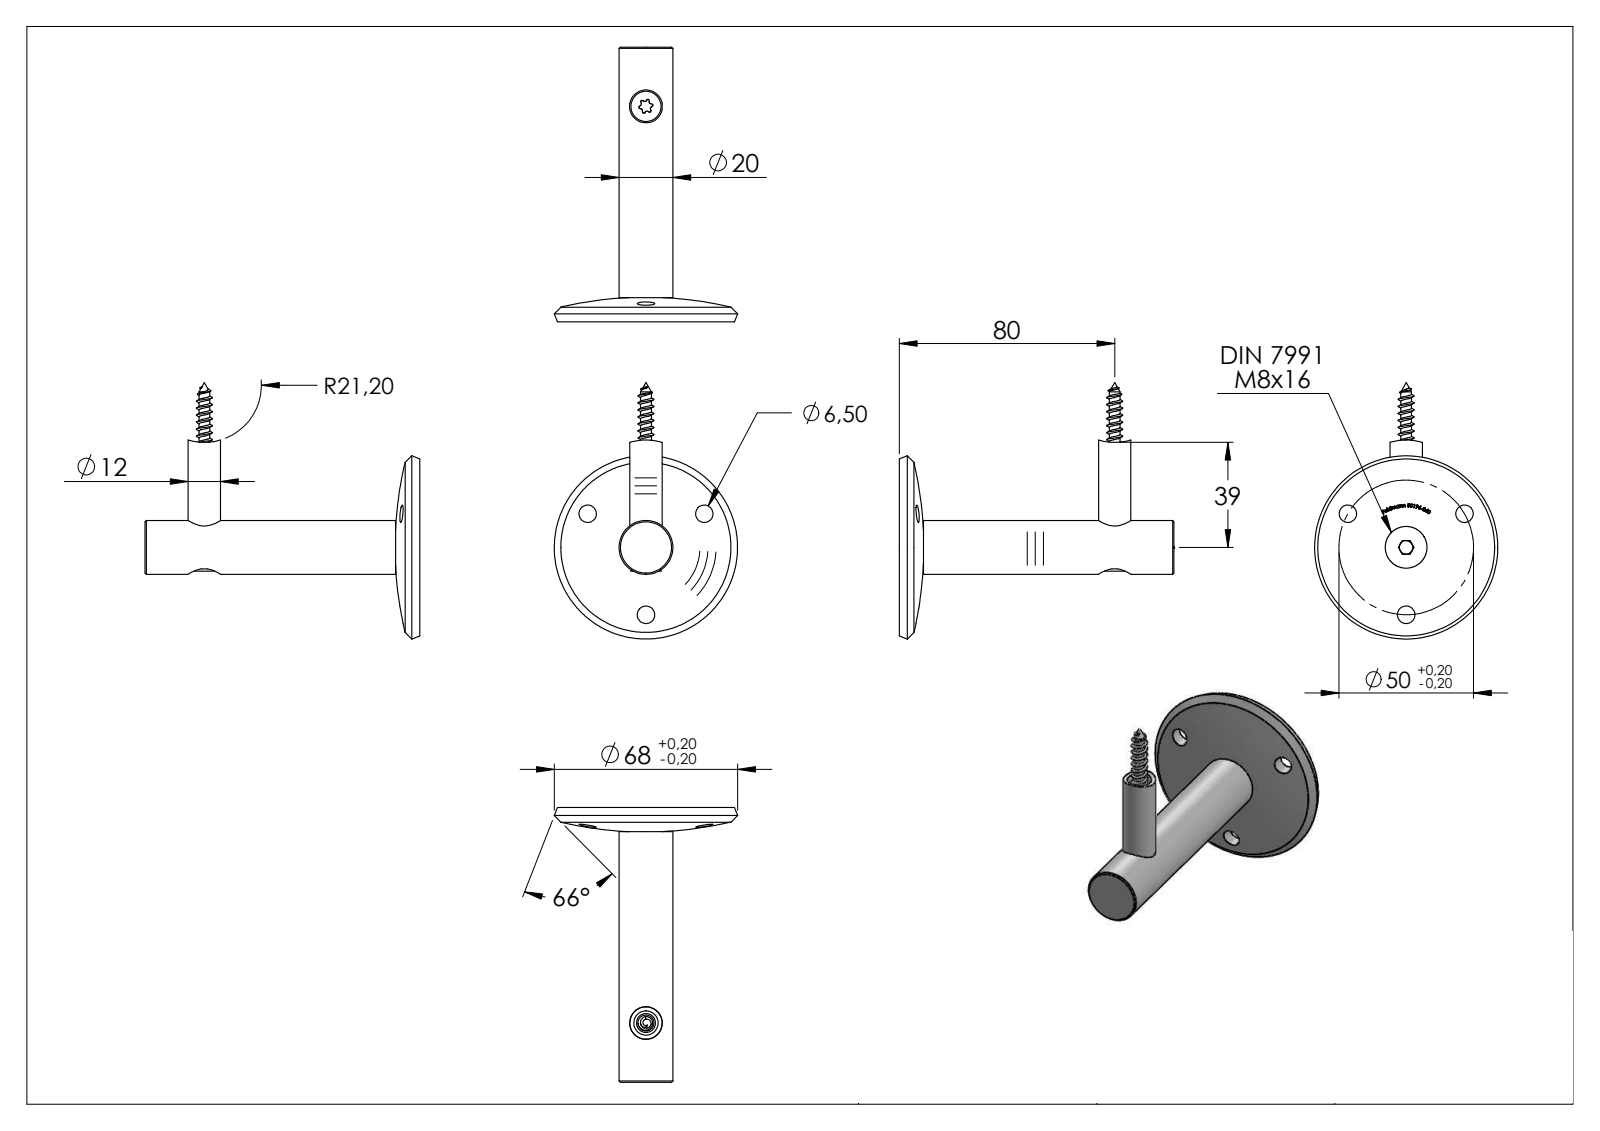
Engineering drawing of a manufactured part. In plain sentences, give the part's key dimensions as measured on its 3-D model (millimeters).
The part is named "50196-240; 50196-240 Teil1; 50196-240 Teil2; socket countersunk head screw_din (+7 more)". Its 3-D file was written by "SolidWorks 2018 (CONFIG_CONTROL_DESIGN)". It is 5 solids with 423 faces: 115 planar, 115 cylindrical and 193 other. Overall it measures 102 by 95.21 by 68 millimeters. Its volume is 47 364 cubic millimeters and its surface area 20 933 square millimeters. Round holes: 3 of diameter 6.5, 1 of diameter 6.8, 1 of diameter 7, 1 of diameter 9, 1 of diameter 12.1, 1 of diameter 12.2, 1 of diameter 12.5. Round bosses or shafts: 2 of diameter 12, 1 of diameter 20, 1 of diameter 15.57, 1 of diameter 11.2, 1 of diameter 8, 1 of diameter 4. Partial cylindrical surfaces (rounded edges, fillets, slot ends): 6 of radius 0.48, 6 of radius 0.84, 1 of radius 21.2. The main face-to-face distances are 100.16, 8.79, 5.16, 95, 16, 10.84, 84.16, 5.02, 2.51, 3.75. The hole center spacings are 25, 43.3.
